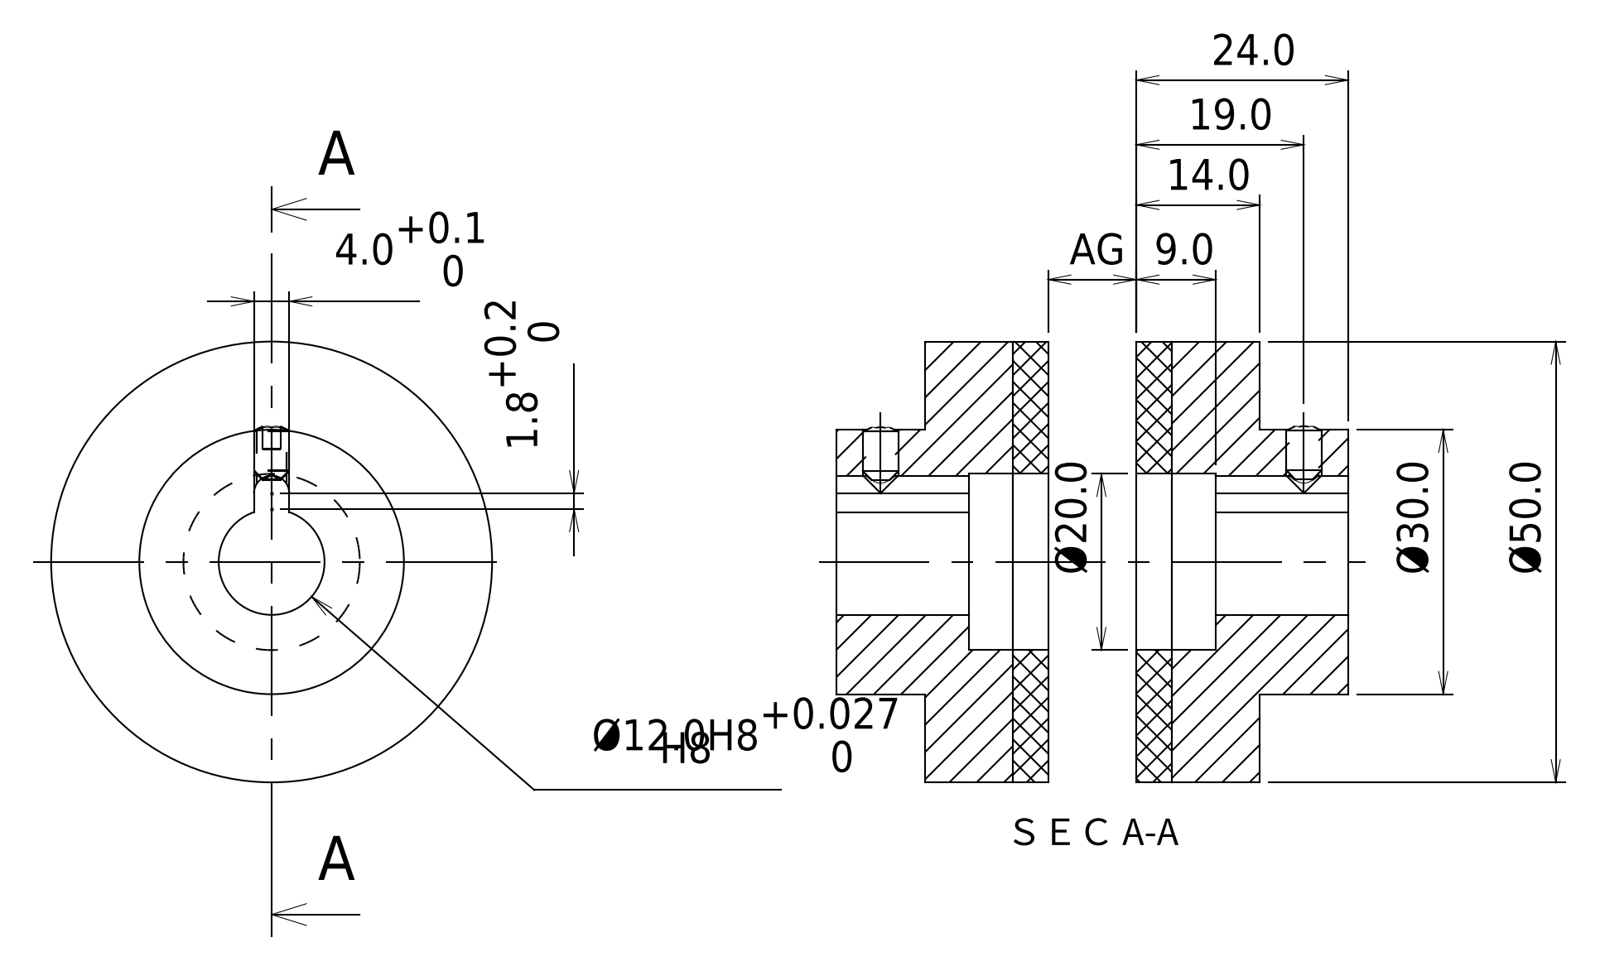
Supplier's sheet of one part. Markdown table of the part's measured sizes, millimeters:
| quantity | value |
| --- | --- |
| STEP written by | PSStep 10.0 (CONFIG_CONTROL_DESIGN) |
| units | millimeters |
| bodies | 4 solids, 38 faces (22 planar, 10 cylindrical, 6 other) |
| overall size | 50 × 50 × 24 |
| volume | 29 895 mm³ |
| surface area | 11 590 mm² |
| round holes (diameter × count) | 3.3 × 1, 12 × 1, 20 × 1 |
| round bosses / shafts (diameter × count) | 50 × 1, 30 × 1, 4 × 1 |
| partial cylindrical surfaces (radius × count) | 2 × 1 |
| main face-to-face distances | 10, 4, 14, 20, 24, 5, 15, 9, 2, 1 |
